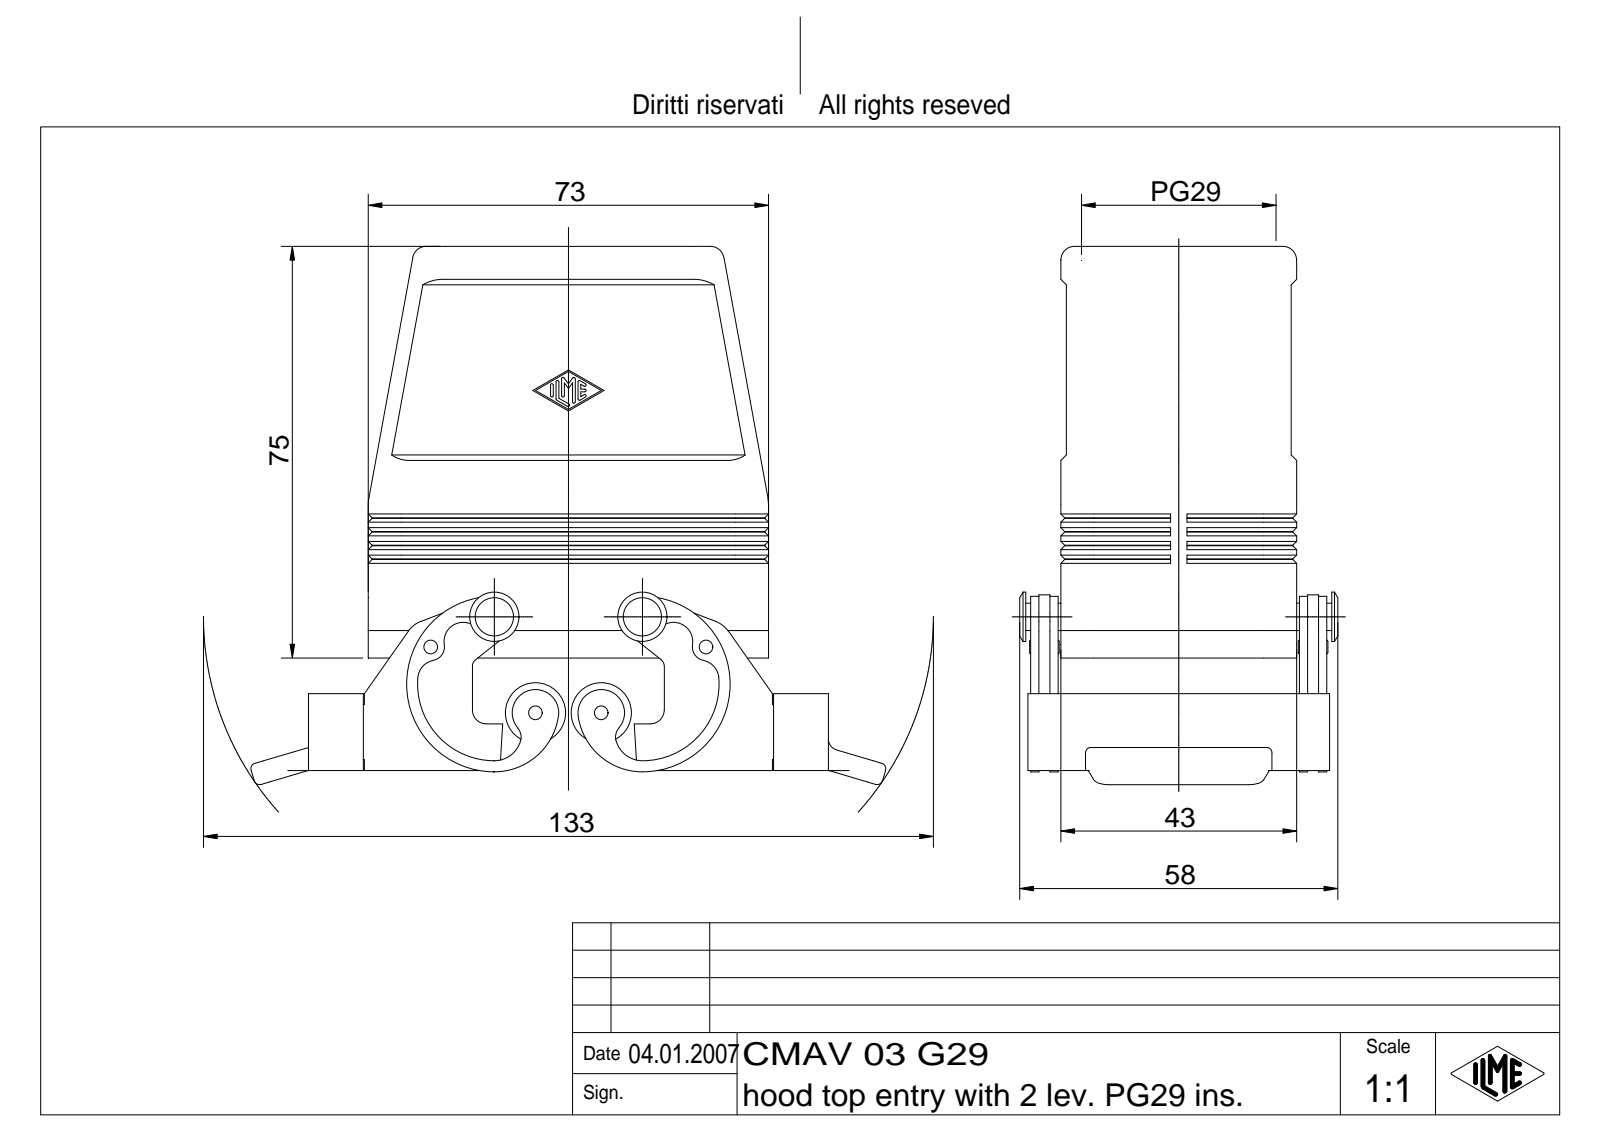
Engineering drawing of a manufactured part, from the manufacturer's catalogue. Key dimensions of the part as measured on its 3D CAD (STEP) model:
Part name (STEP PRODUCT): CAV Tüllengehäuse 2 Bügel für einen Einsatz
STEP written by: Autodesk Inventor 7 (AUTOMOTIVE_DESIGN)
Units: millimetres
Bodies: 1 solid, 835 faces (258 planar, 222 cylindrical, 355 other)
Overall size (bounding box): 115.79 × 98.08 × 58
Volume: 84 543 mm³ · Surface area: 49 680 mm²
Round holes (diameter × count): ⌀2.5 ×2, ⌀35.48 ×1
Round bosses / shafts (diameter × count): ⌀11 ×2, ⌀9 ×2, ⌀5 ×2, ⌀2 ×2
Partial cylindrical surfaces — rounded edges, fillets, slot ends (radius × count): R0.25 ×14, R1 ×12, R2.5 ×10, R6 ×10, R3 ×8, R2 ×7, R3.5 ×4, R5 ×4
Main face-to-face distances: 4, 3, 39, 38, 35, 1, 42, 43, 41, 2
Hole centre spacings: 50.2
